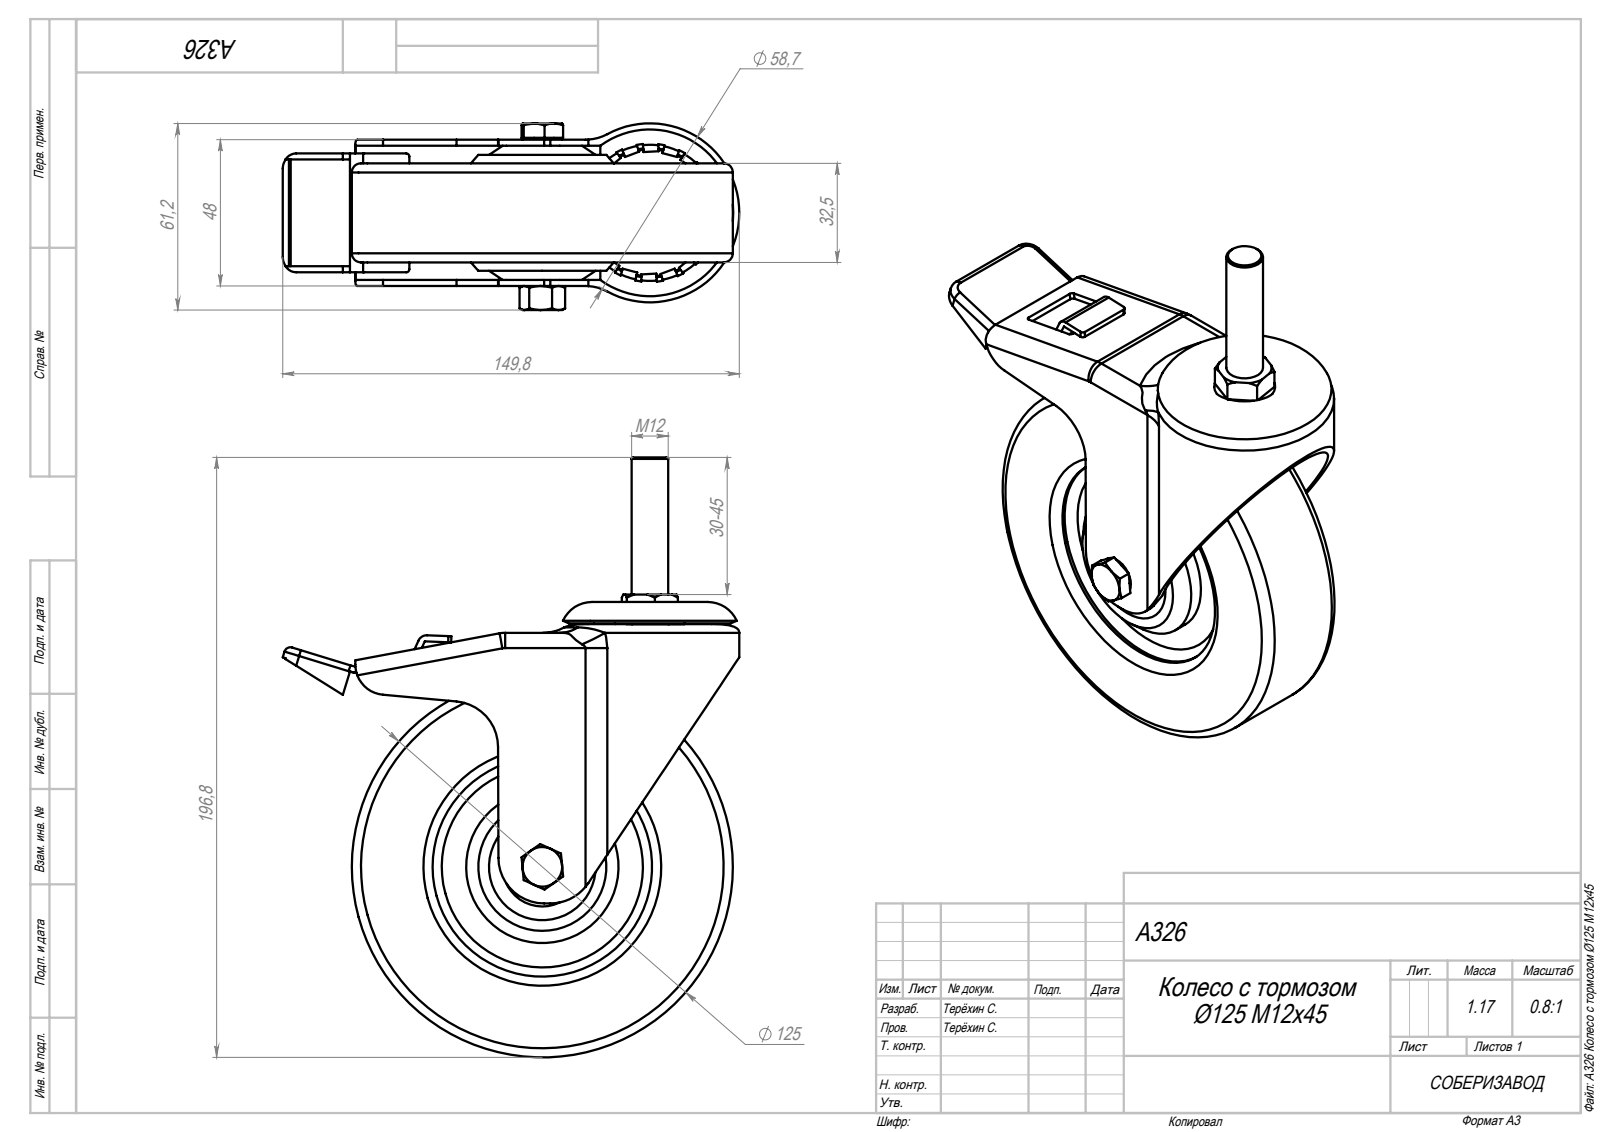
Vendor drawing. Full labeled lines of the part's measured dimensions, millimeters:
Part name (STEP PRODUCT): Болт_00; Тормоз_00; A326 Колесо с тормозом O125 М12х45; Дно_00 (+6 more)
STEP written by: SolidWorks 2018 (AUTOMOTIVE_DESIGN)
Units: millimetres
Bodies: 10 solids, 399 faces (182 planar, 78 cylindrical, 139 other)
Overall size (bounding box): 196.78 × 149.8 × 61.25
Volume: 412 327 mm³ · Surface area: 105 904 mm²
Round holes (diameter × count): ⌀6.8 ×1, ⌀8 ×1, ⌀12 ×1, ⌀46 ×1, ⌀72 ×1
Round bosses / shafts (diameter × count): ⌀125 ×1, ⌀50 ×1, ⌀13 ×1
Partial cylindrical surfaces — rounded edges, fillets, slot ends (radius × count): R1 ×6, R2 ×6, R5 ×6, R15 ×5, R10 ×4, R3 ×1, R27.35 ×1, R29.35 ×1
Main face-to-face distances: 2, 7, 5.75, 38.25, 12.75, 31.25, 25.5, 7.75, 33.25, 32.5
